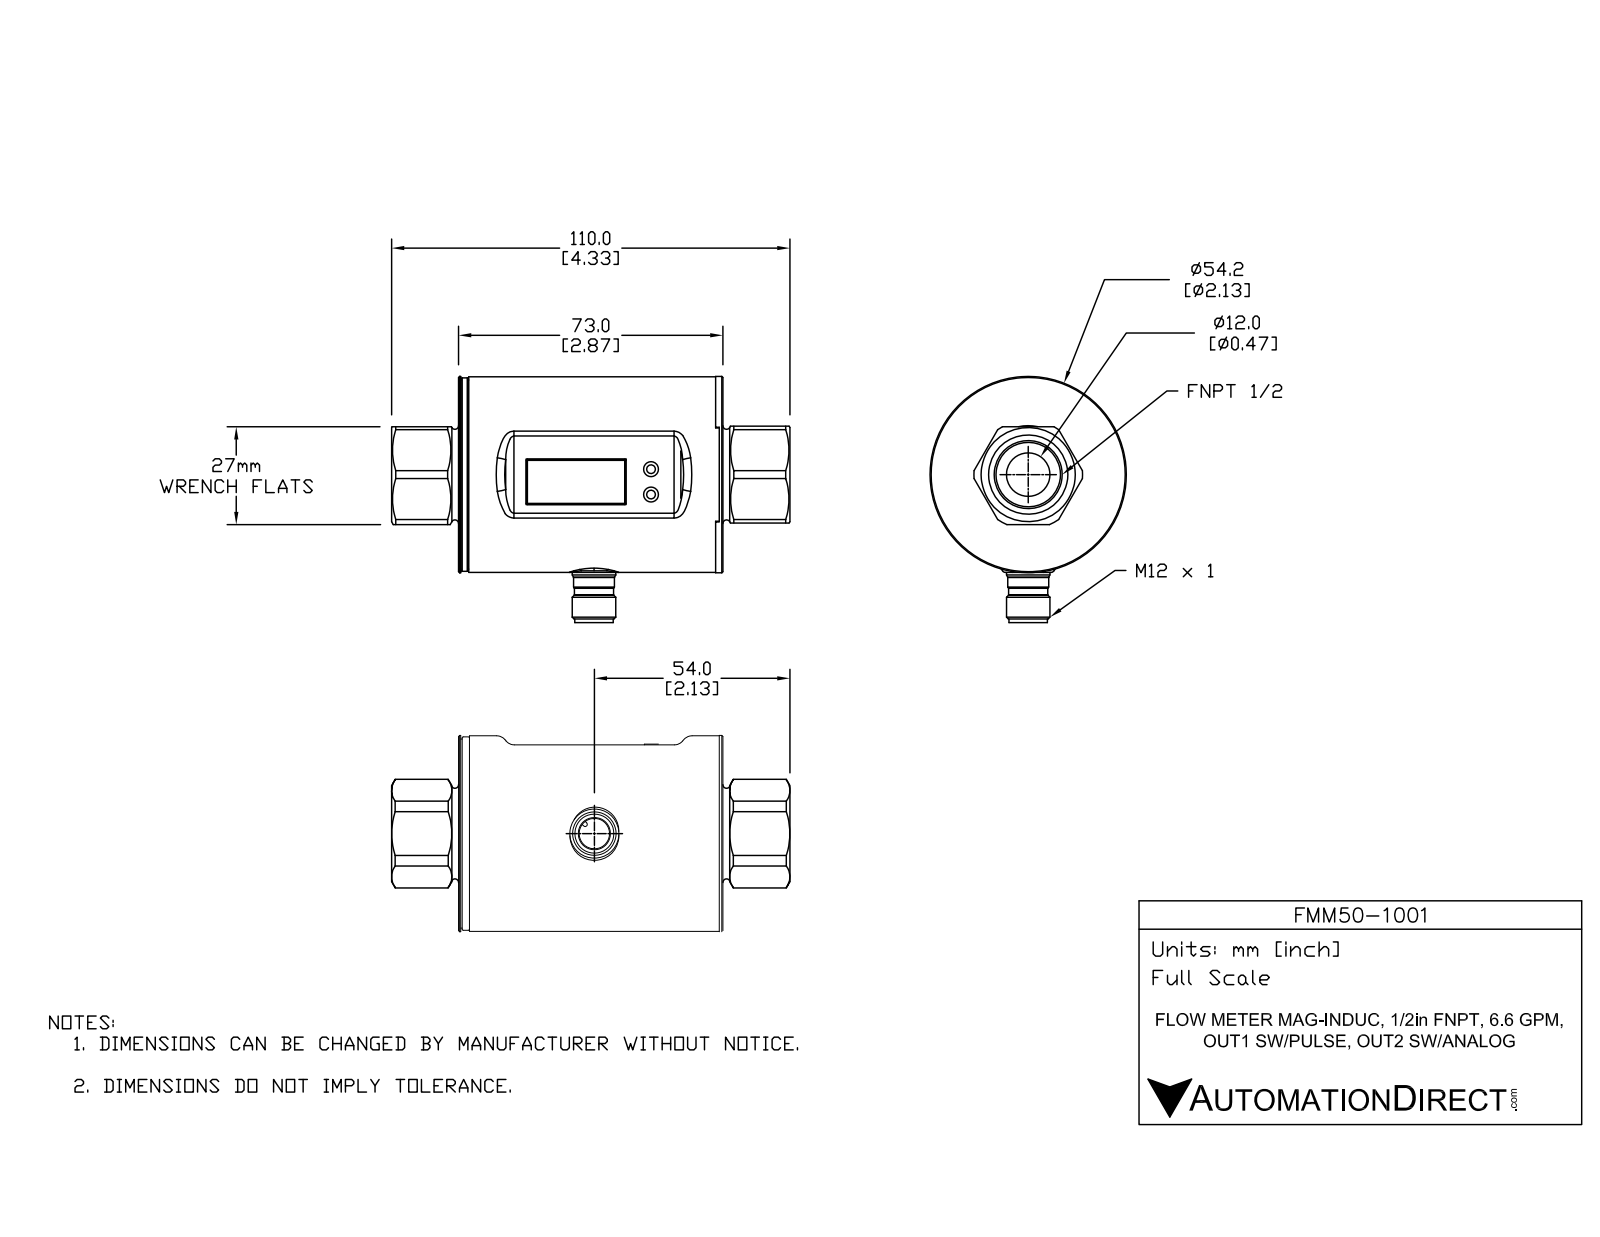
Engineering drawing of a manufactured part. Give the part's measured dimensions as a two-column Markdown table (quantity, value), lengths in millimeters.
| quantity | value |
| --- | --- |
| part name | FMM50-1001 |
| STEP written by | SolidWorks 2015 (AUTOMOTIVE_DESIGN) |
| units | millimeters |
| bodies | 12 solids, 226 faces (90 planar, 97 cylindrical, 39 other) |
| overall size | 109.99 × 67.85 × 54.2 |
| volume | 54 735 mm³ |
| surface area | 55 987 mm² |
| round holes (diameter × count) | 1.5 × 2, 3.6 × 2, 4.11 × 2, 6.2 × 1, 8 × 1, 8.4 × 1, 12 × 1, 18.79 × 1, 52 × 1 |
| round bosses / shafts (diameter × count) | 3.9 × 2, 54.2 × 1, 54 × 1, 53.4 × 1, 52.2 × 1, 27 × 1, 12 × 1, 11.3 × 1 |
| partial cylindrical surfaces (radius × count) | 1 × 4, 0.3 × 2, 2 × 2, 3 × 2, 0.6 × 1, 15 × 1 |
| main face-to-face distances | 70, 2, 71.7, 1, 72, 72.7, 73, 8.2, 64.5, 63.5 |
| hole center spacings | 13, 1.25, 7, 8, 9.25, 21, 22.25, 26 |
